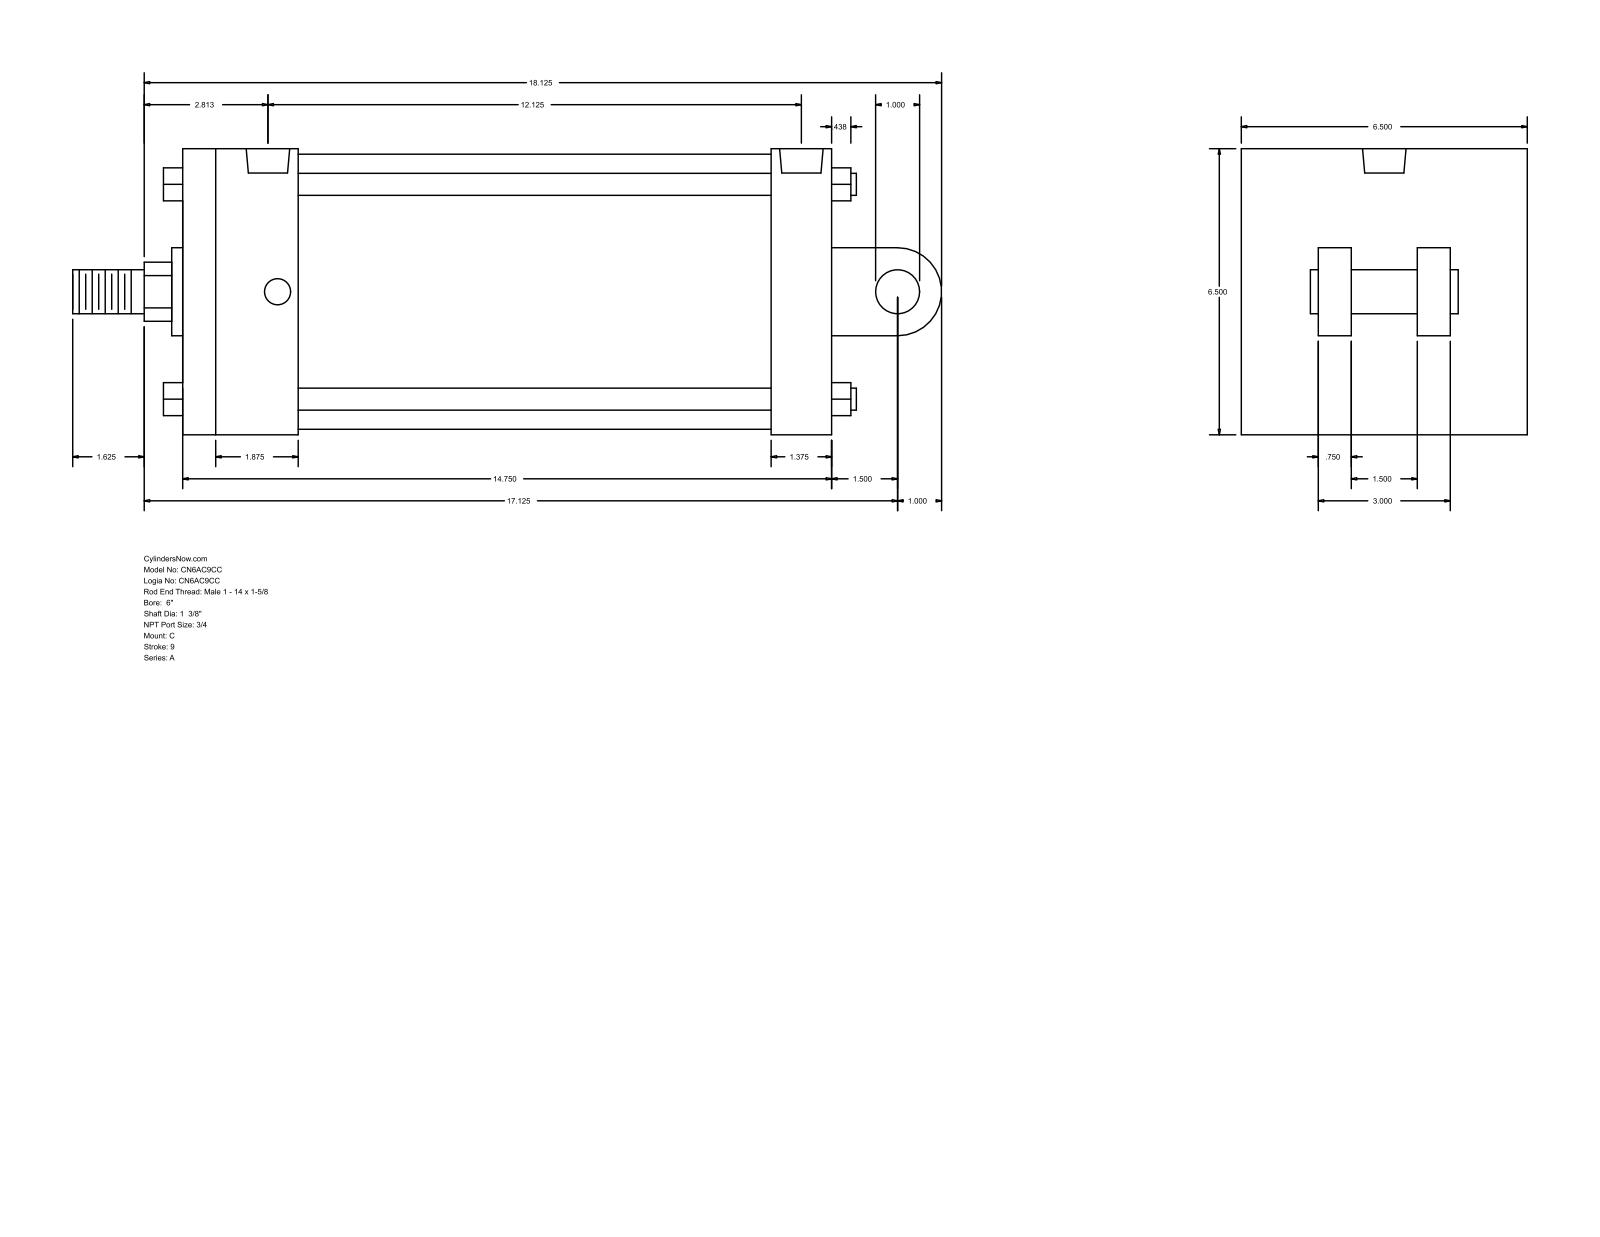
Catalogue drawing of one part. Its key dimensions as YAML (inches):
part_name: "A_C__0600_1.375"
step_written_by: "GSSL Pune (CONFIG_CONTROL_DESIGN)"
units: inches
bodies: {solids: 0, faces: 135, planar: 102, cylindrical: 33, other: 0}
overall_size: [19.75, 6.5, 6.5]
round_holes:
  - {diameter: 0.594, count: 4}
  - {diameter: 0.989, count: 2}
round_bosses_or_shafts:
  - {diameter: 0.5, count: 4}
  - {diameter: 1, count: 2}
  - {diameter: 6.25, count: 1}
  - {diameter: 2, count: 1}
  - {diameter: 1.375, count: 1}
partial_cylinders:
  - {radius: 0.672, count: 1}
  - {radius: 1, count: 1}
face_to_face_distances: [6.5, 14.75, 2.25, 0.75, 2.625, 12.125, 13.375, 10.75, 1.375, 2.5]
hole_center_spacings: [0.219, 11.687, 11.906, 12.125]
